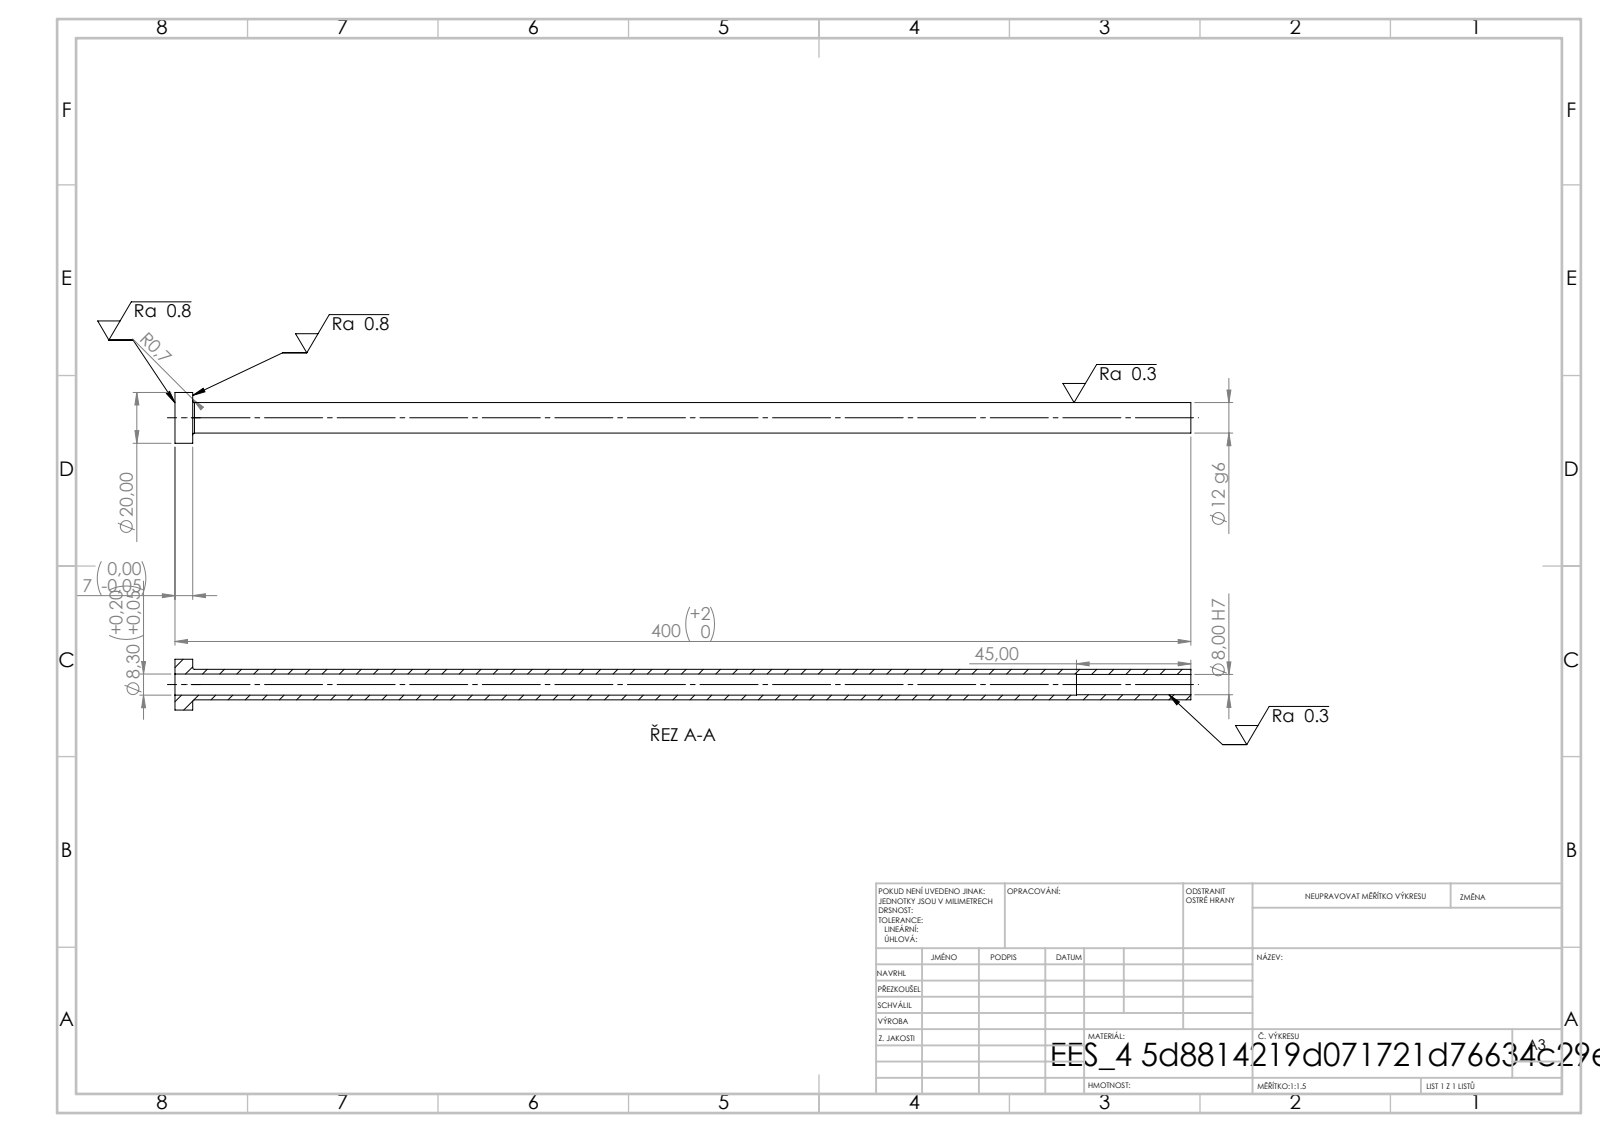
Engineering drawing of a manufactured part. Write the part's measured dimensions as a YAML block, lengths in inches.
step_written_by: "SolidWorks 2019 (CONFIG_CONTROL_DESIGN)"
units: inches
bodies: {solids: 1, faces: 14, planar: 4, cylindrical: 8, other: 2}
overall_size: [15.748, 0.787, 0.787]
volume: 1.537
surface_area: 40.55
round_holes:
  - {diameter: 0.315, count: 1}
  - {diameter: 0.327, count: 1}
round_bosses_or_shafts:
  - {diameter: 0.787, count: 1}
  - {diameter: 0.472, count: 1}
face_to_face_distances: [0.276, 15.748, 15.472, 13.976, 13.701, 1.772]
